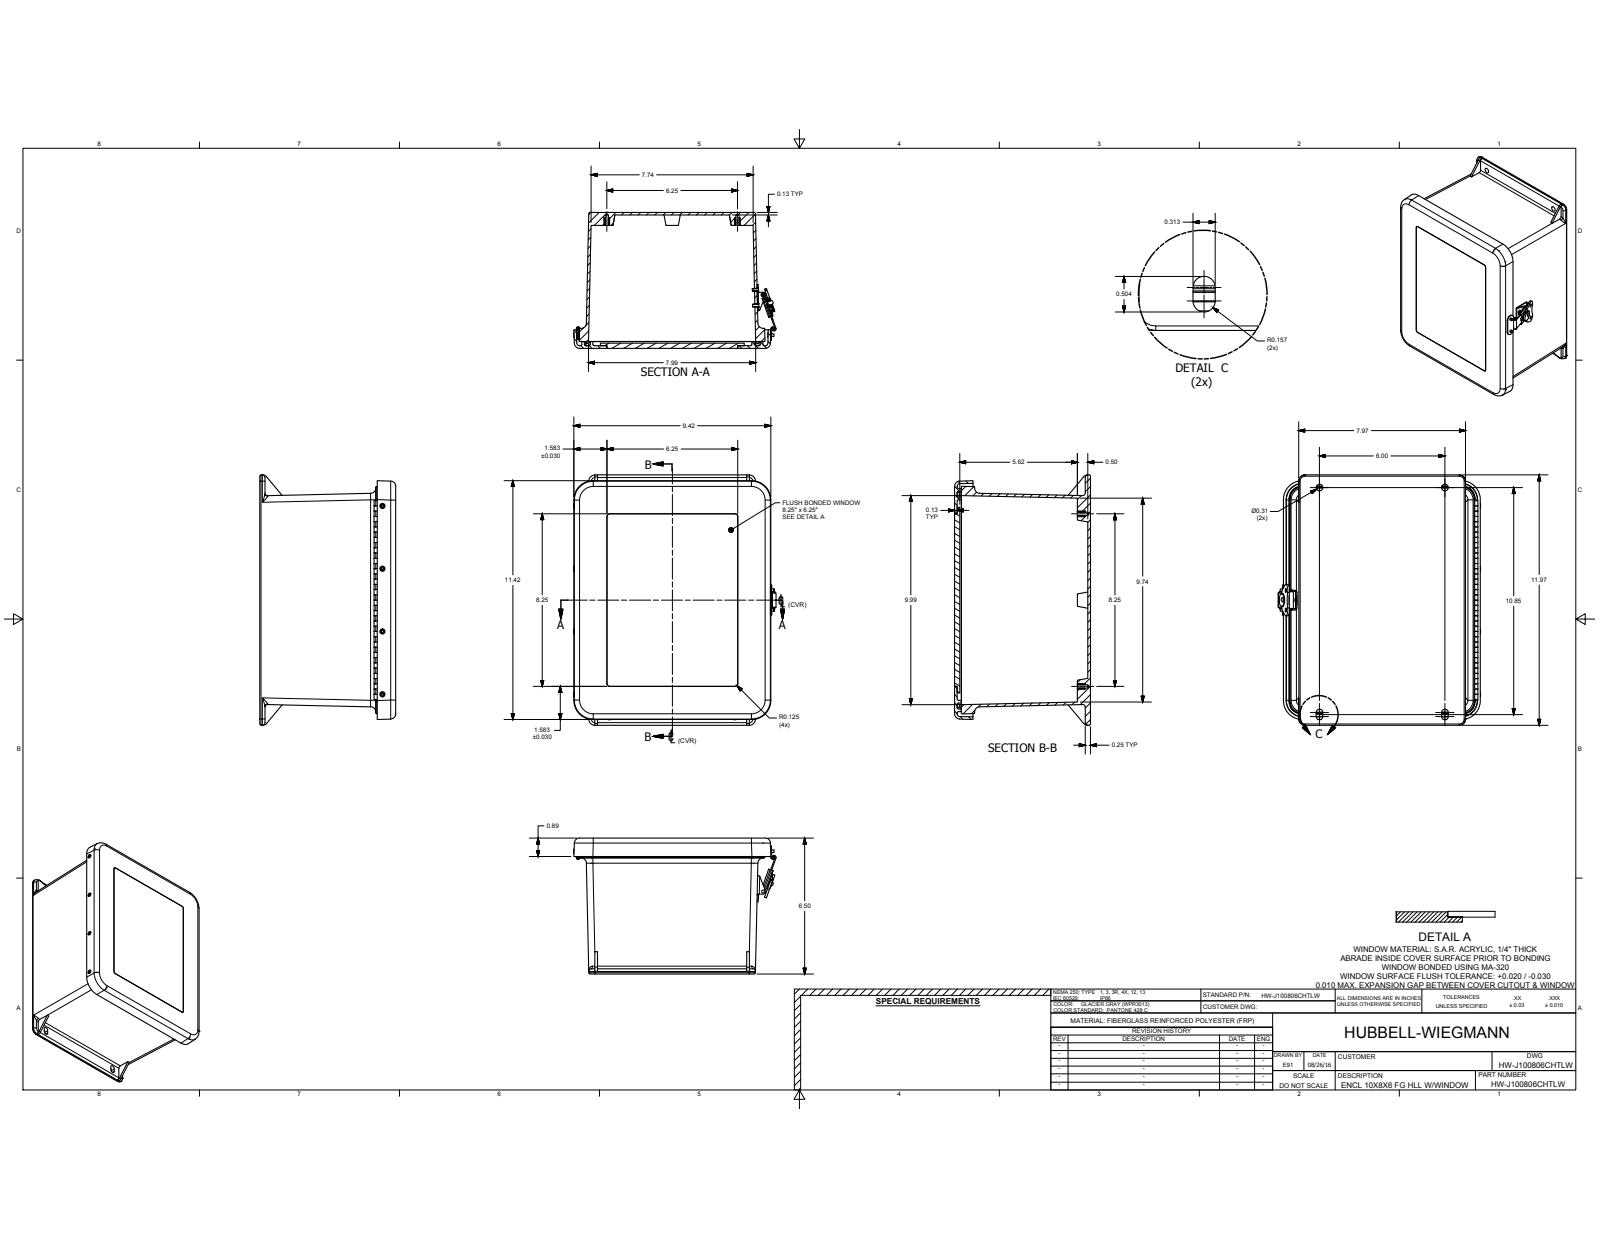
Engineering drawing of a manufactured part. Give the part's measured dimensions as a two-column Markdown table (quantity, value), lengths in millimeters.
| quantity | value |
| --- | --- |
| part name | HW-J100806CHTLW; WPJ100806H&LBOX; WPJW100806HL; WPJ100806H&LCVR (+8 more) |
| STEP written by | Autodesk Inventor 2017 (CONFIG_CONTROL_DESIGN) |
| units | millimeters |
| bodies | 41 solids, 1216 faces (482 planar, 473 cylindrical, 261 other) |
| overall size | 303.94 × 245.78 × 165.1 |
| volume | 1 379 000 mm³ |
| surface area | 683 194 mm² |
| round holes (diameter × count) | 3.56 × 13, 2.64 × 12, 3.86 × 12, 4.04 × 12, 3.33 × 8, 9.52 × 4, 3.3 × 2, 3.38 × 2, 4.75 × 2, 7.95 × 2, 1.7 × 1, 2.16 × 1 |
| round bosses / shafts (diameter × count) | 6.86 × 12, 3.17 × 12, 16.76 × 1, 14.78 × 1, 13.34 × 1, 7.26 × 1, 5.41 × 1, 4.57 × 1 |
| partial cylindrical surfaces (radius × count) | 1.59 × 34, 0.79 × 26, 3.17 × 23, 1.6 × 20, 1 × 16, 7.62 × 12, 6.35 × 11, 0.38 × 8 |
| main face-to-face distances | 3.11, 3.17, 161.93, 165.1, 158.75, 6.35, 155.58, 3.18, 158.76, 5.16 |
| hole center spacings | 152.4, 76.2, 63.5, 88.9, 215.9, 0.32, 228.6, 3.17 |
